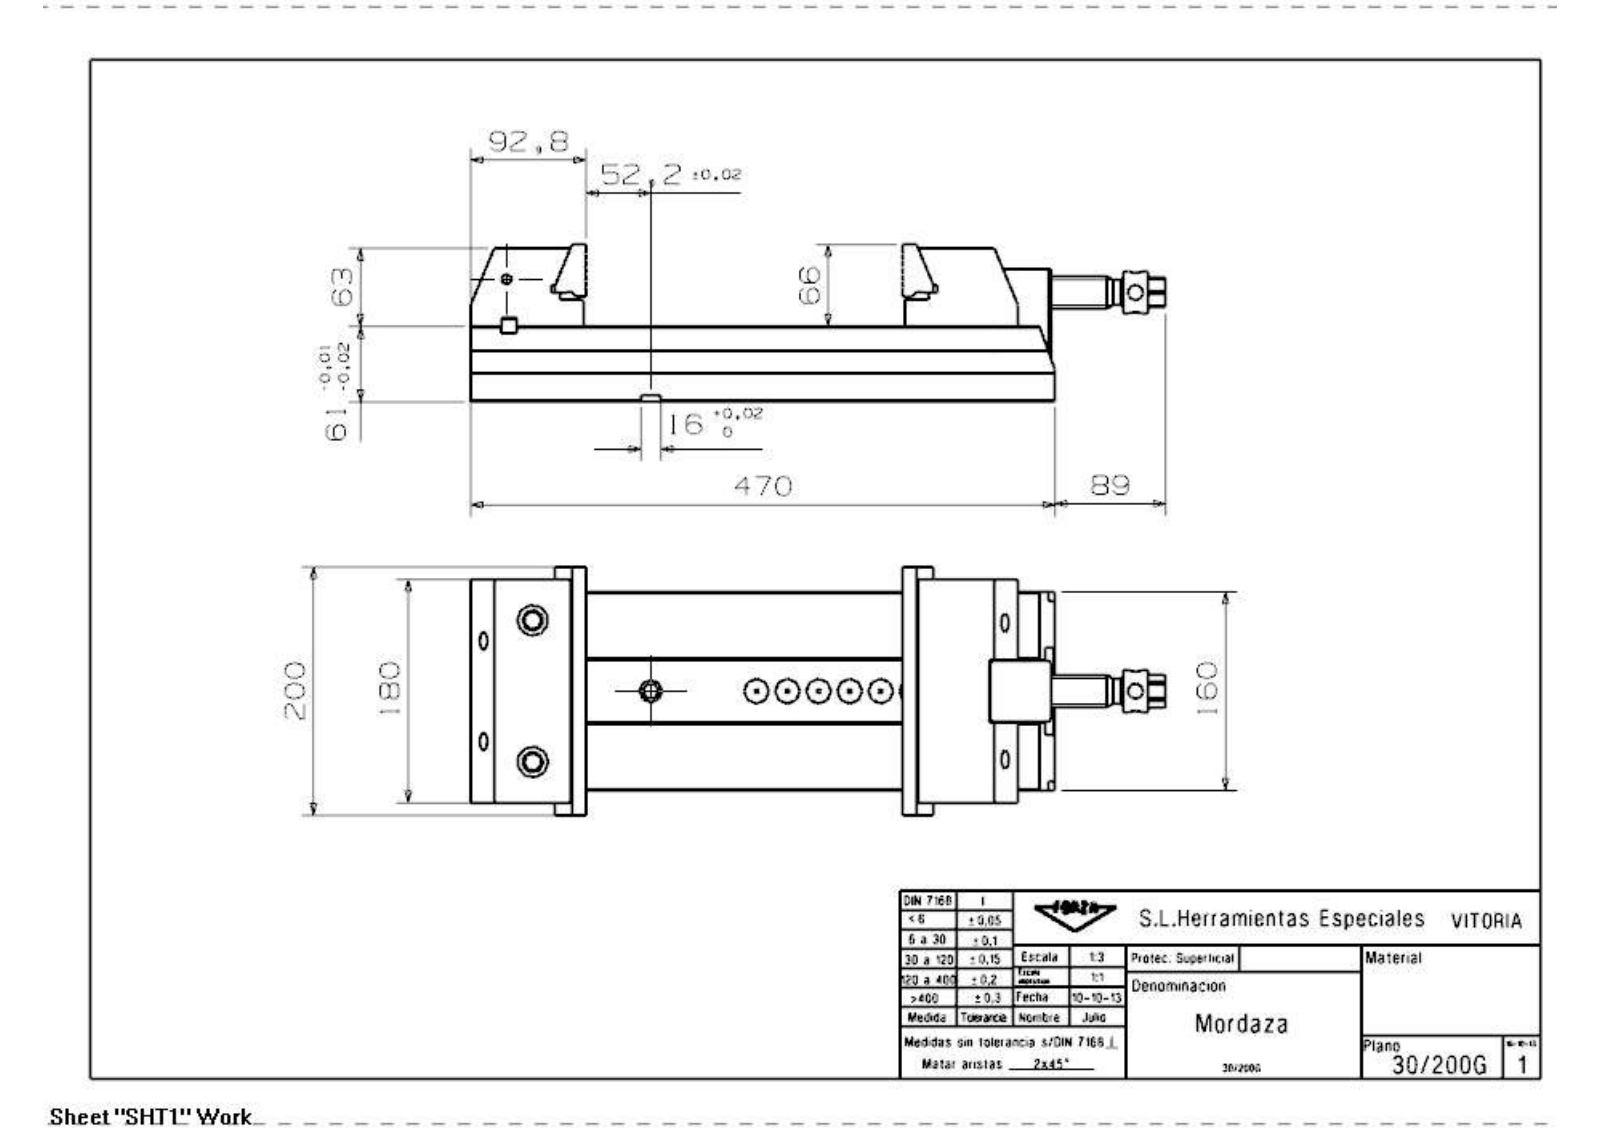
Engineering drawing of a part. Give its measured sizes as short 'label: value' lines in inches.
name: 30150070 Montaje Taco Hus; 30_200G_Mordaza
written by: SIEMENS PLM Software NX 7.5 (CONFIG_CONTROL_DESIGN)
unit: in
bodies: 12 solids, 500 faces (303 planar, 132 cylindrical, 65 other)
size: 22.008 × 7.874 × 4.998
volume: 337 in³; area: 917.6 in²
holes: 6× ⌀0.591, 5× ⌀0.204, 5× ⌀0.512, 4× ⌀0.275, 4× ⌀0.335, 4× ⌀0.394, 4× ⌀0.566, 3× ⌀0.346, 3× ⌀0.748, 2× ⌀0.472, 2× ⌀0.487, 2× ⌀0.669
bosses: 1× ⌀1.339, 1× ⌀1.331, 1× ⌀1.024, 1× ⌀0.787, 1× ⌀0.65
rounds: 24× R0.016, 4× R0.315, 4× R0.787, 2× R0.063, 2× R0.236, 2× R0.276, 1× R0.157, 1× R0.354
face distances: 2.402, 1.15, 1.252, 4.882, 3.732, 2.48, 0.394, 6.299, 0.043, 1.106
hole spacings: 0.571, 3.76, 3.189, 4.331, 0.648, 0.652, 0.965, 1.181
